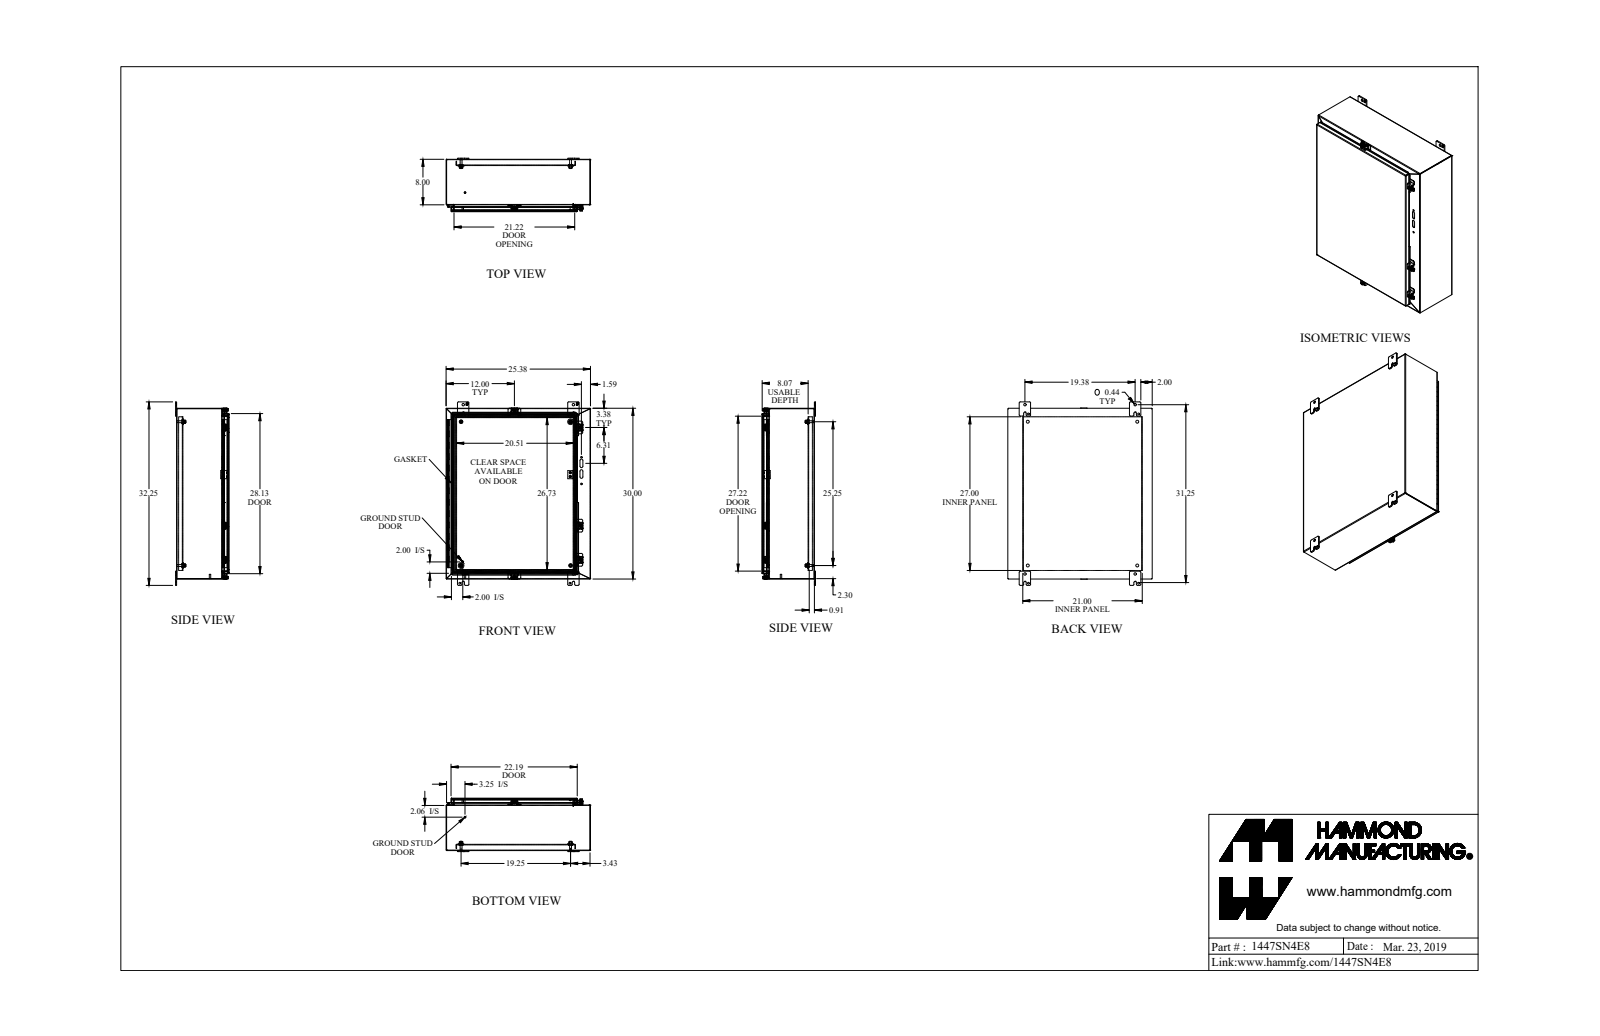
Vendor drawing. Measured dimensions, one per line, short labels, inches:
name: 1447SN4E8_Default
written by: SolidWorks 2019 (CONFIG_CONTROL_DESIGN)
unit: in
bodies: 46 solids, 1639 faces (972 planar, 573 cylindrical, 94 other)
size: 32.25 × 25.375 × 9.397
volume: 266.5 in³; area: 6 974 in²
holes: 6× ⌀0.313, 5× ⌀0.213, 5× ⌀0.265, 5× ⌀0.375, 4× ⌀0.437, 4× ⌀0.5, 2× ⌀0.15, 2× ⌀0.156, 2× ⌀0.281, 2× ⌀0.307, 2× ⌀0.445, 1× ⌀0.187
bosses: 5× ⌀0.5, 5× ⌀0.39, 5× ⌀0.244, 4× ⌀0.65, 4× ⌀0.375, 4× ⌀0.33, 4× ⌀0.25, 2× ⌀1
rounds: 28× R0.25, 27× R0.048, 27× R0.143, 24× R0.188, 23× R0.036, 23× R0.108, 10× R0.045, 10× R0.141
face distances: 0.072, 9.066, 9.138, 0.072, 9.138, 9.21, 0.095, 8.106, 8.034, 1.032
hole spacings: 21.146, 19.375, 1.736, 2.122, 9.612, 12.155, 19.25, 22.252
